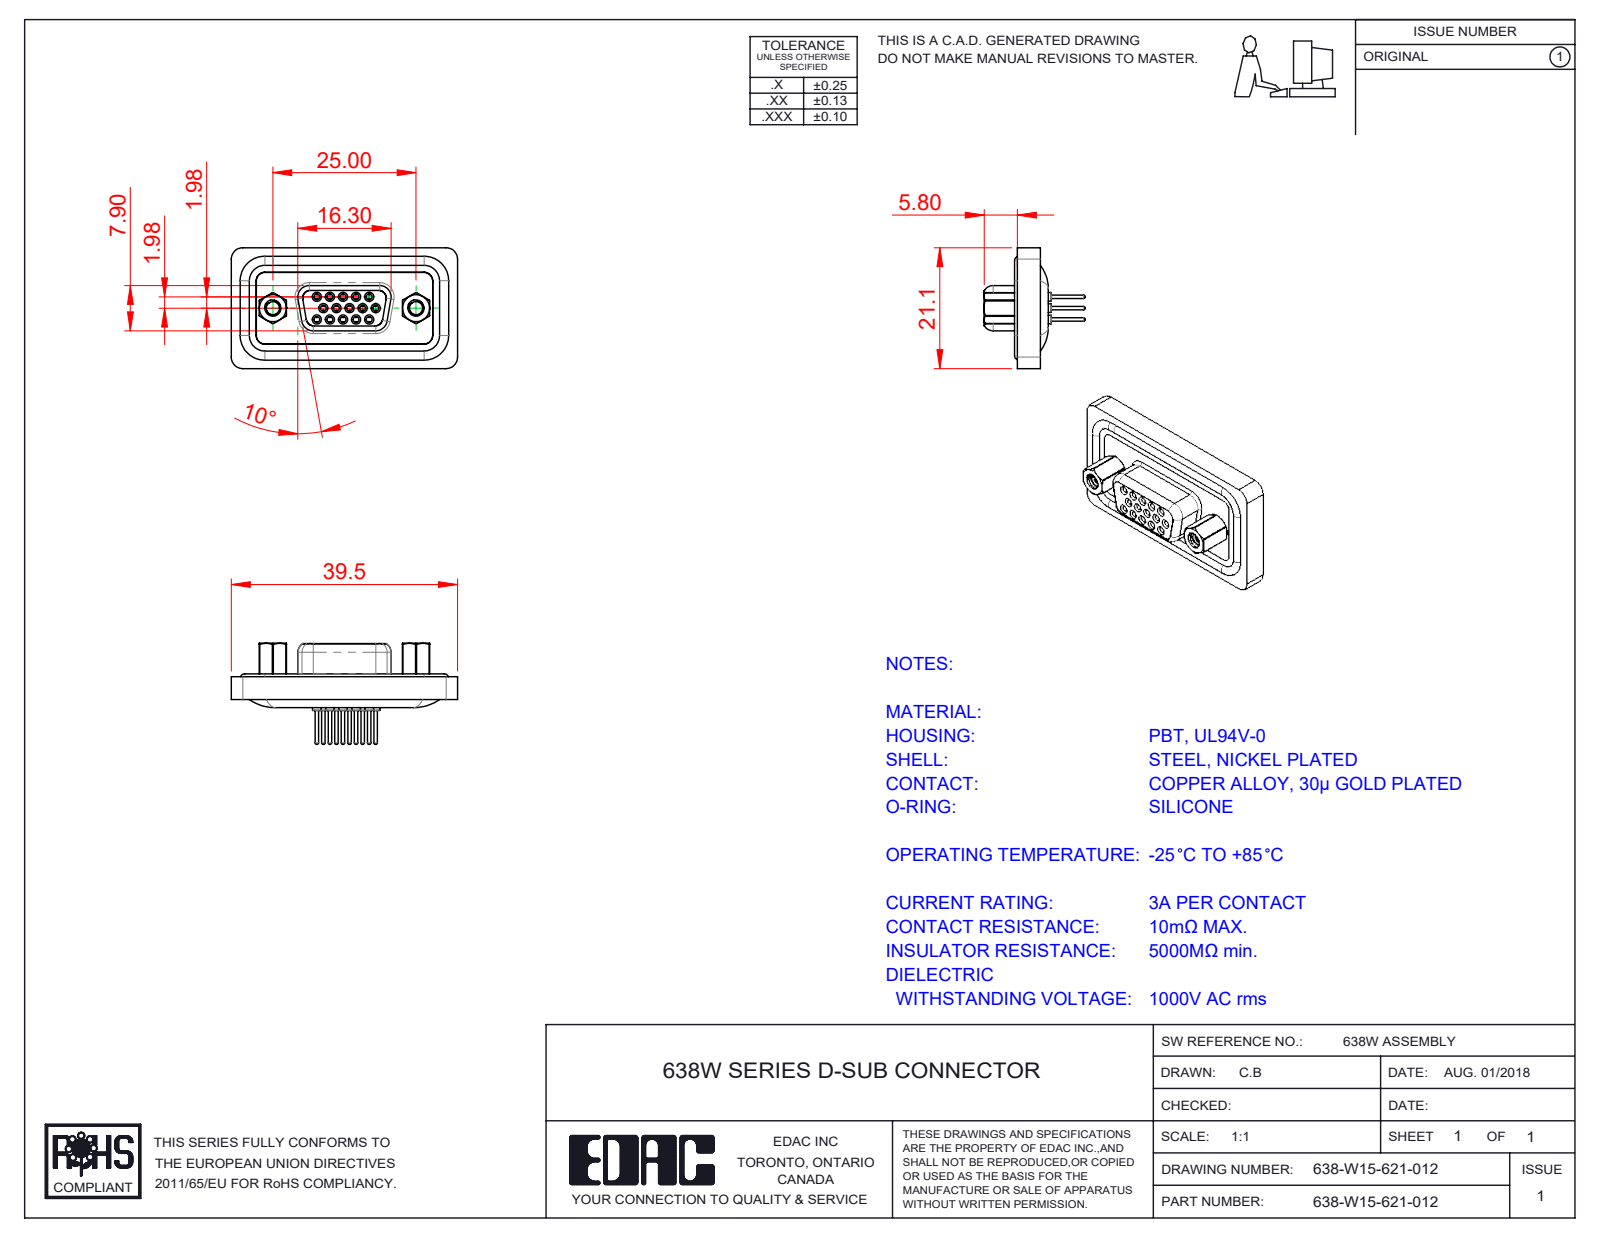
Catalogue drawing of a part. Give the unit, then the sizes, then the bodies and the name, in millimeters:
Units: millimetres
Overall size (bounding box): 39.51 × 21.1 × 17.65
Round holes (diameter × count): ⌀1 ×15, ⌀1.1 ×15, ⌀1.5 ×15, ⌀1.7 ×15, ⌀1.8 ×15, ⌀2 ×15, ⌀2.26 ×2, ⌀2.29 ×2, ⌀4 ×2, ⌀4.8 ×2, ⌀5 ×2
Round bosses / shafts (diameter × count): ⌀1.6 ×19, ⌀2.2 ×15, ⌀0.6 ×15, ⌀1.5 ×6, ⌀4.9 ×2, ⌀2.79 ×2, ⌀5 ×1
Partial cylindrical surfaces — rounded edges, fillets, slot ends (radius × count): R1.5 ×14, R2 ×14, R1.35 ×8, R2.7 ×6, R0.5 ×4, R0.9 ×4, R1.6 ×4, R1.75 ×4
Main face-to-face distances: 0.4, 2.9, 1.6, 1.1, 2.5, 1.8, 0.5, 3.6, 0.7, 4
Hole centre spacings: 2.28, 3.96, 2.29, 4.57, 6.05, 6.04, 3.95, 8.24
Volume: 4 326 mm³ · Surface area: 8 103 mm²
Bodies: 23 solids, 1276 faces (326 planar, 531 cylindrical, 419 other)
Part name (STEP PRODUCT): 638-W15-621-012; 638W 4-40 Threaded Rivet; 638W Contact Row 3_21; 638W Contact Row 2_21 (+5 more)
STEP written by: SolidWorks 2016 (CONFIG_CONTROL_DESIGN)
